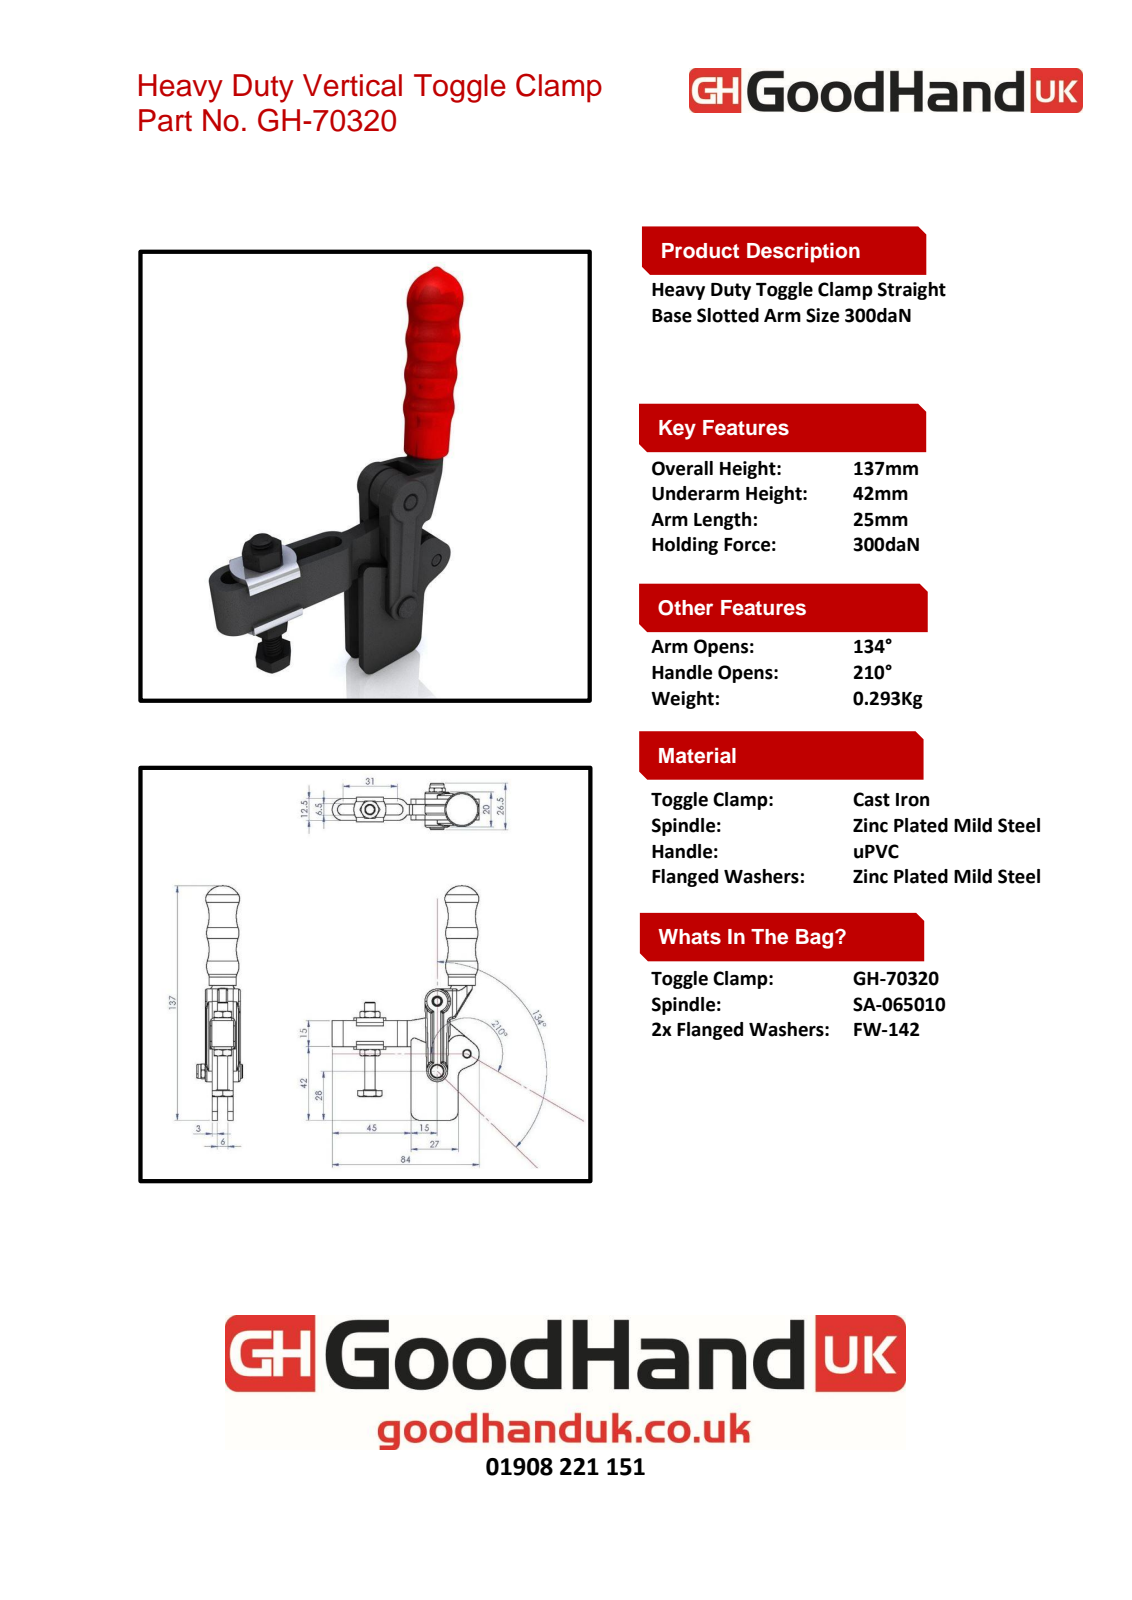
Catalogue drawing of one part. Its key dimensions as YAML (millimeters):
part_name: "Group2^GH-70320(簡化)-1; Group1^GH-70320(簡化)-1; 4701608-1^GH-70320(簡化)-1; Group5^GH-70320(簡化)-1 (+2 more)"
step_written_by: "SolidWorks 2016 (AUTOMOTIVE_DESIGN)"
units: millimeters
bodies: {solids: 5, faces: 327, planar: 114, cylindrical: 100, other: 113}
overall_size: [134.02, 84, 23.95]
volume: 43426
surface_area: 24734
round_holes:
  - {diameter: 4, count: 4}
round_bosses_or_shafts:
  - {diameter: 14, count: 1}
  - {diameter: 7.5, count: 1}
  - {diameter: 6, count: 1}
partial_cylinders:
  - {radius: 1, count: 23}
  - {radius: 5, count: 5}
  - {radius: 2.6, count: 4}
  - {radius: 2, count: 3}
  - {radius: 7, count: 3}
  - {radius: 3.25, count: 2}
  - {radius: 6, count: 2}
  - {radius: 6.25, count: 2}
face_to_face_distances: [3, 9, 12, 6, 9.25, 4, 13, 7, 16, 13.25]
hole_center_spacings: [18, 19.72, 20.43, 22.02, 34.55, 40]
